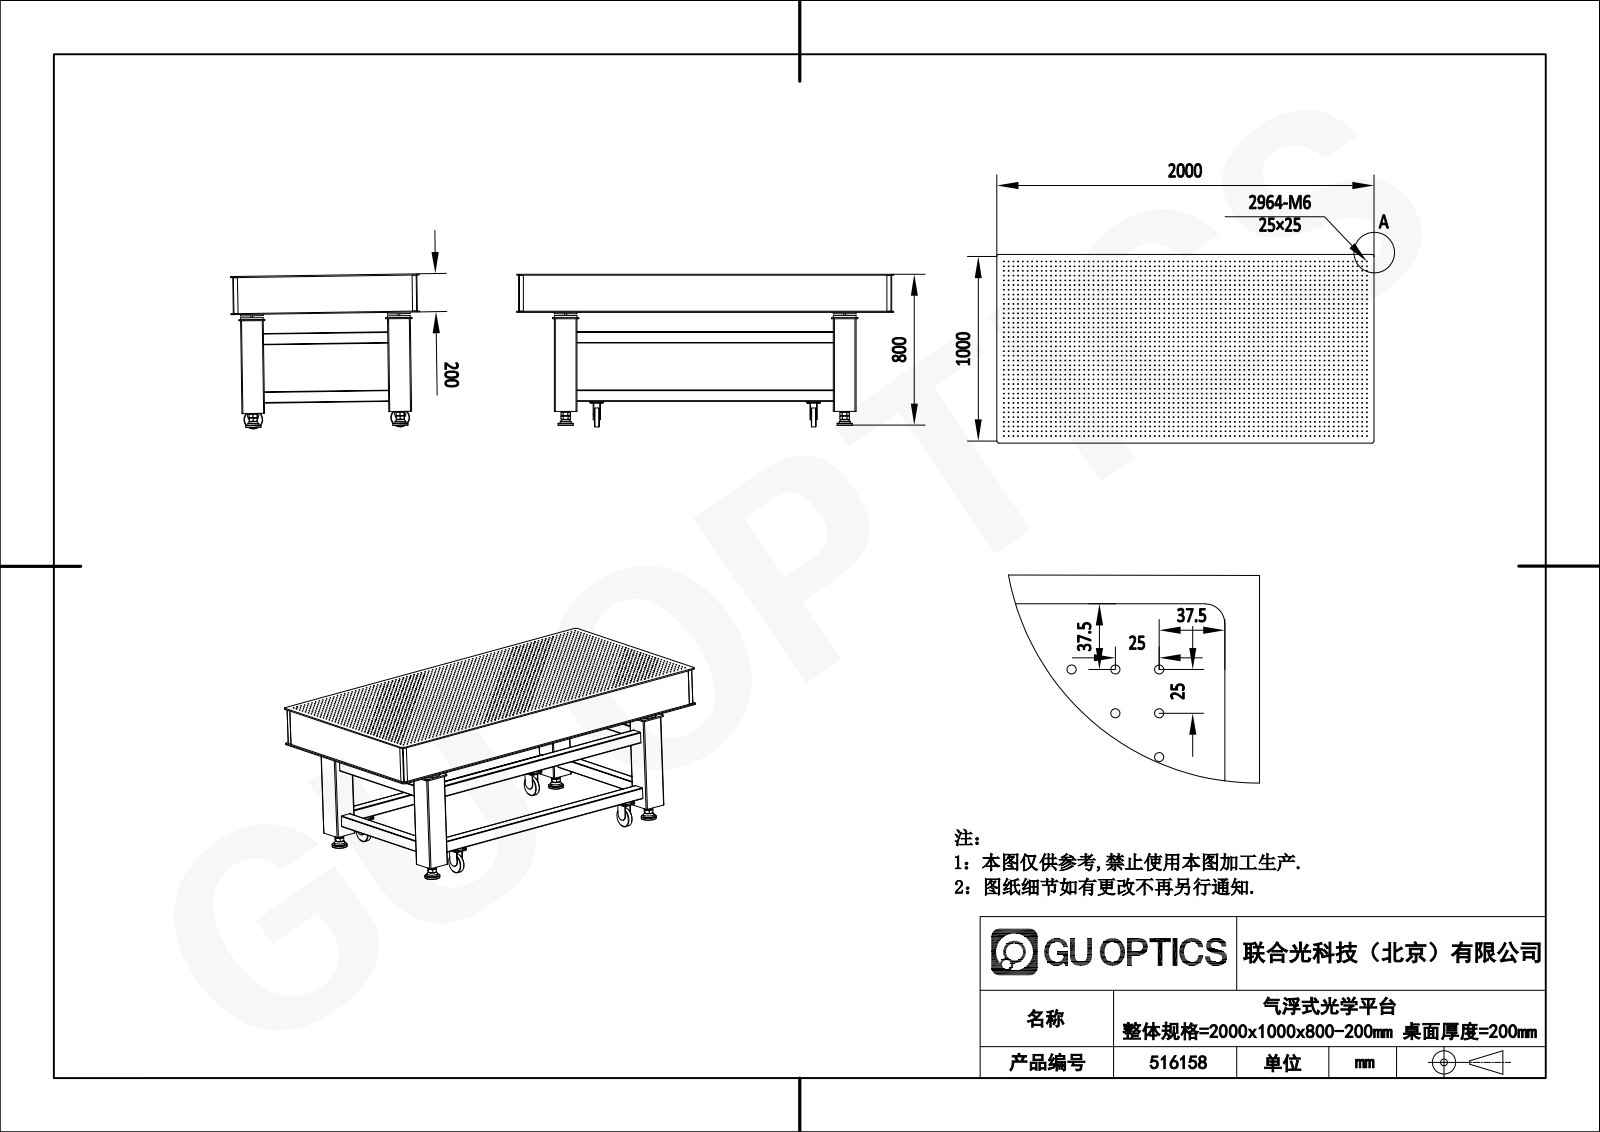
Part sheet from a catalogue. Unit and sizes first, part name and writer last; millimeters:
Units: millimetres
Overall size (bounding box): 2000 × 1000 × 810
Round holes (diameter × count): ⌀5.3 ×2964, ⌀8.5 ×16, ⌀9 ×16, ⌀17.5 ×4, ⌀22 ×4, ⌀28 ×4, ⌀43 ×4
Round bosses / shafts (diameter × count): ⌀120 ×4, ⌀80 ×4, ⌀58 ×4, ⌀14 ×4, ⌀10 ×4, ⌀100 ×2
Partial cylindrical surfaces — rounded edges, fillets, slot ends (radius × count): R1 ×48, R10 ×48, R3 ×36, R5 ×16, R7 ×16, R2 ×4, R11 ×4, R30 ×2
Main face-to-face distances: 5, 197, 202, 2, 58, 780, 307, 56, 60, 309
Hole centre spacings: 50, 100, 150, 200, 250, 300, 350, 400
Volume: 399 500 000 mm³ · Surface area: 16 030 000 mm²
Bodies: 61 solids, 9933 faces (3453 planar, 6288 cylindrical, 192 other)
Part name (STEP PRODUCT): 516158
STEP written by: SolidWorks 2020 (CONFIG_CONTROL_DESIGN)
